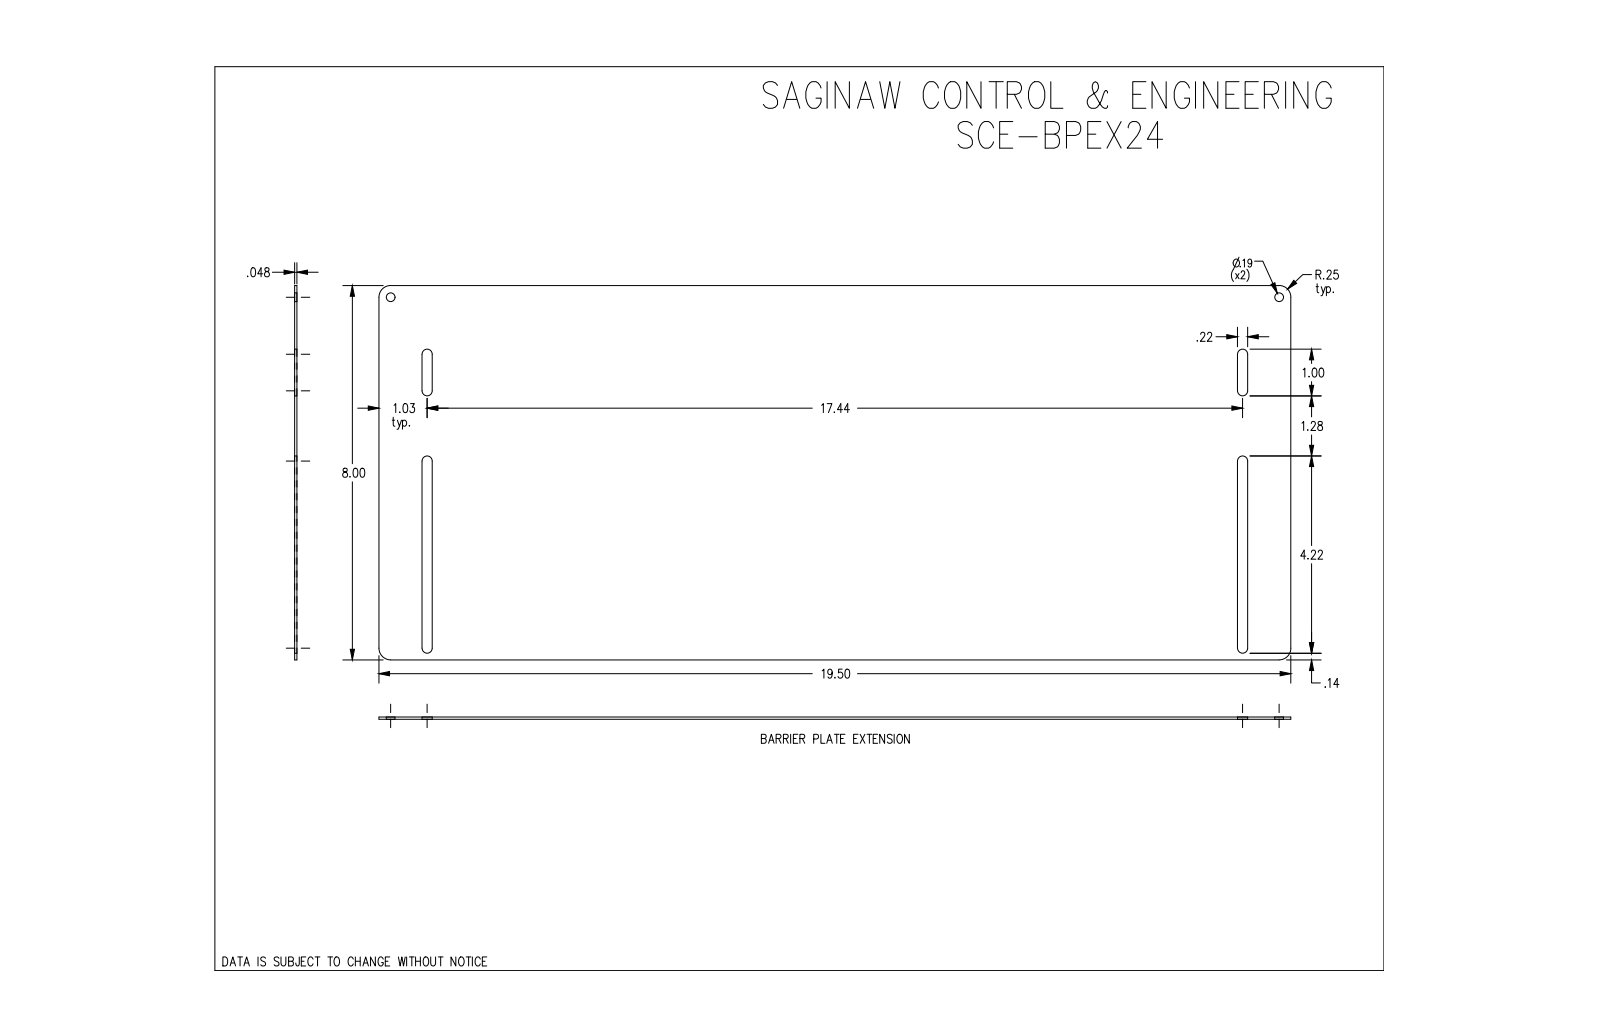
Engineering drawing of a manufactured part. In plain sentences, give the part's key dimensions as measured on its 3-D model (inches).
The part is named "SCE-BPEX24". Its 3-D file was written by "SolidWorks 2019 (CONFIG_CONTROL_DESIGN)". It is 1 solid with 28 faces: 14 planar, 14 cylindrical and 0 other. Overall it measures 19.5 by 8 by 0.048 inches. Its volume is 7.376 cubic inches and its surface area 311 square inches. Round holes: 2 of diameter 0.187. Partial cylindrical surfaces (rounded edges, fillets, slot ends): 8 of radius 0.109, 4 of radius 0.25. The main face-to-face distances are 0.048, 8, 0.922, 1.14, 18.36, 18.578, 0.218, 17.437, 19.5, 17.655. The hole center spacings are 19.
